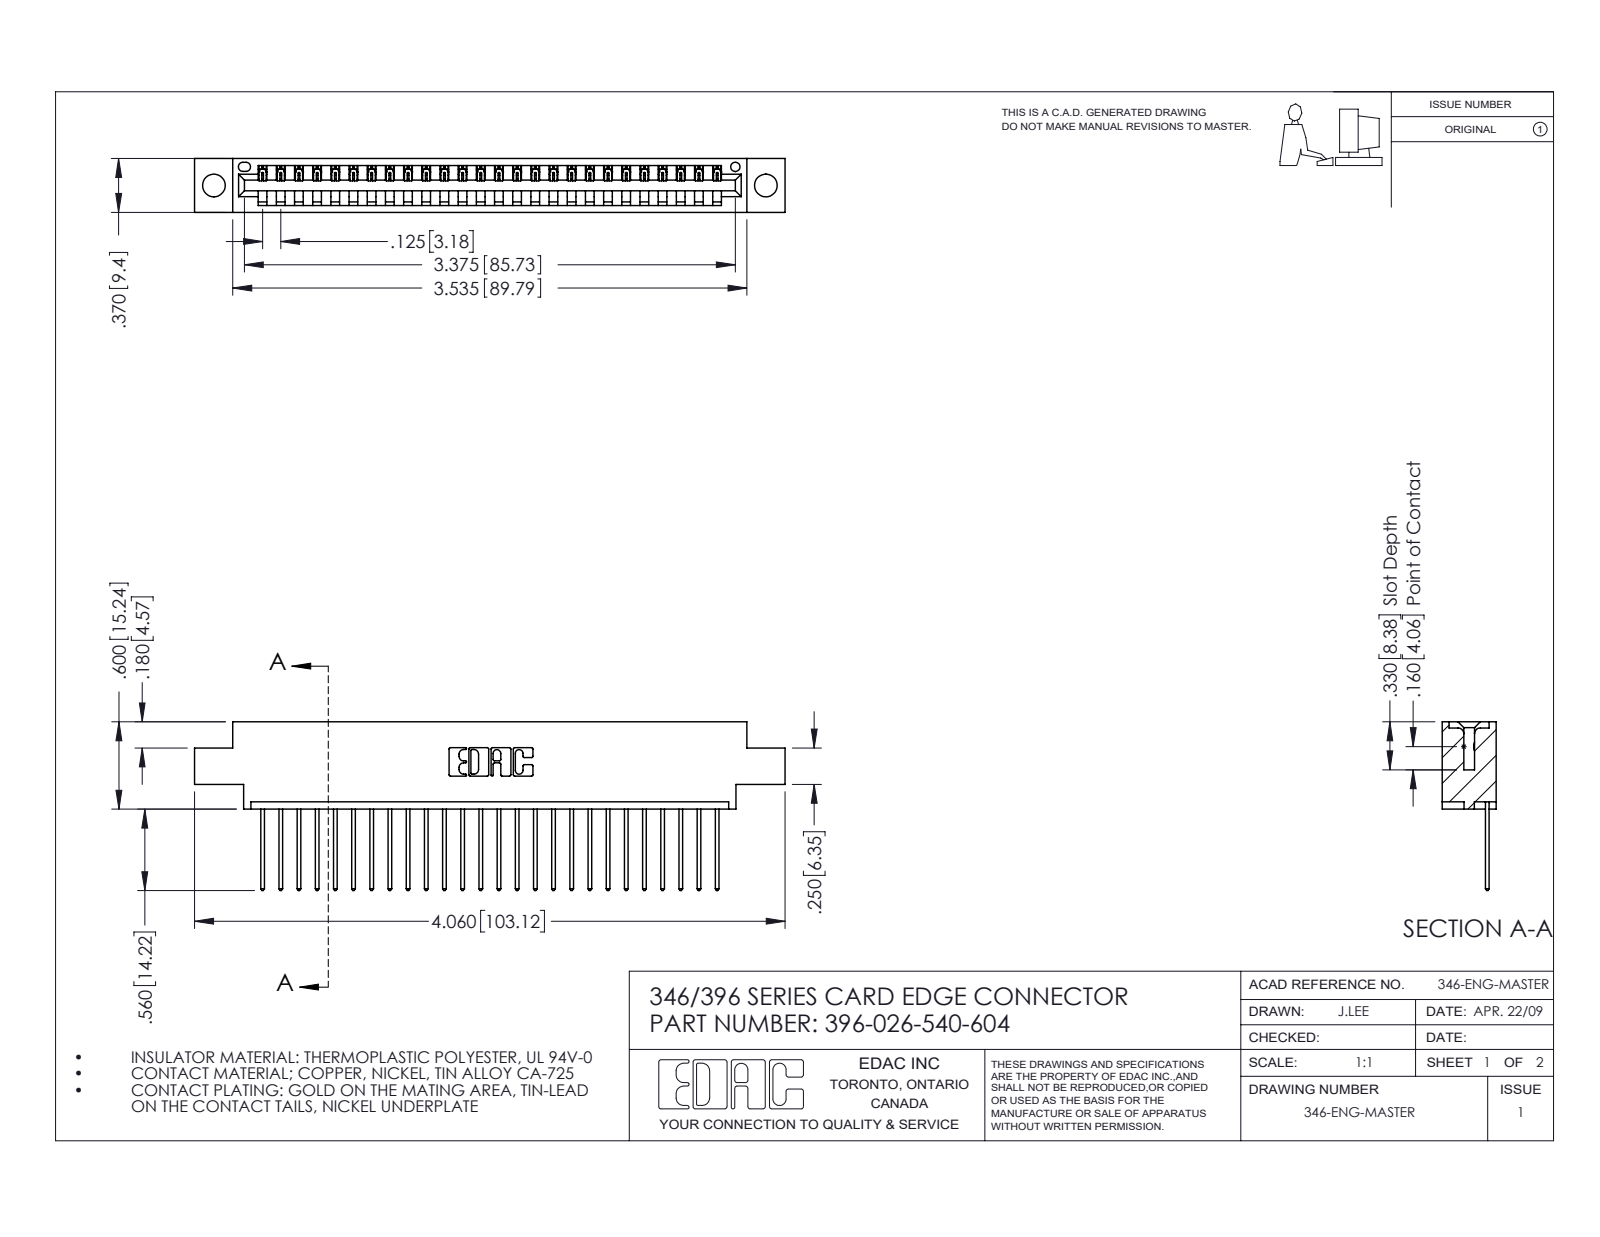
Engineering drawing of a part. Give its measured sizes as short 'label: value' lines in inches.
name: 396-026-540-604; 345-292-001_345-293-140; 346 Part_0.170 Offset - 0.156 Dia-TH
written by: SolidWorks 2016 (CONFIG_CONTROL_DESIGN)
unit: in
bodies: 27 solids, 1634 faces (1120 planar, 514 cylindrical, 0 other)
size: 4.06 × 1.16 × 0.37
volume: 0.583 in³; area: 18.59 in²
holes: 2× ⌀0.156, 1× ⌀0.064
rounds: 52× R0.006, 52× R0.01, 22× R0.01, 6× R0.007, 6× R0.031, 3× R0.026, 2× R0.031, 2× R0.04
face distances: 0.048, 0.322, 0.37, 0.25, 0.072, 0.298, 0.025, 0.148, 0.222, 0.1
hole spacings: 0.246, 3.587, 3.795
